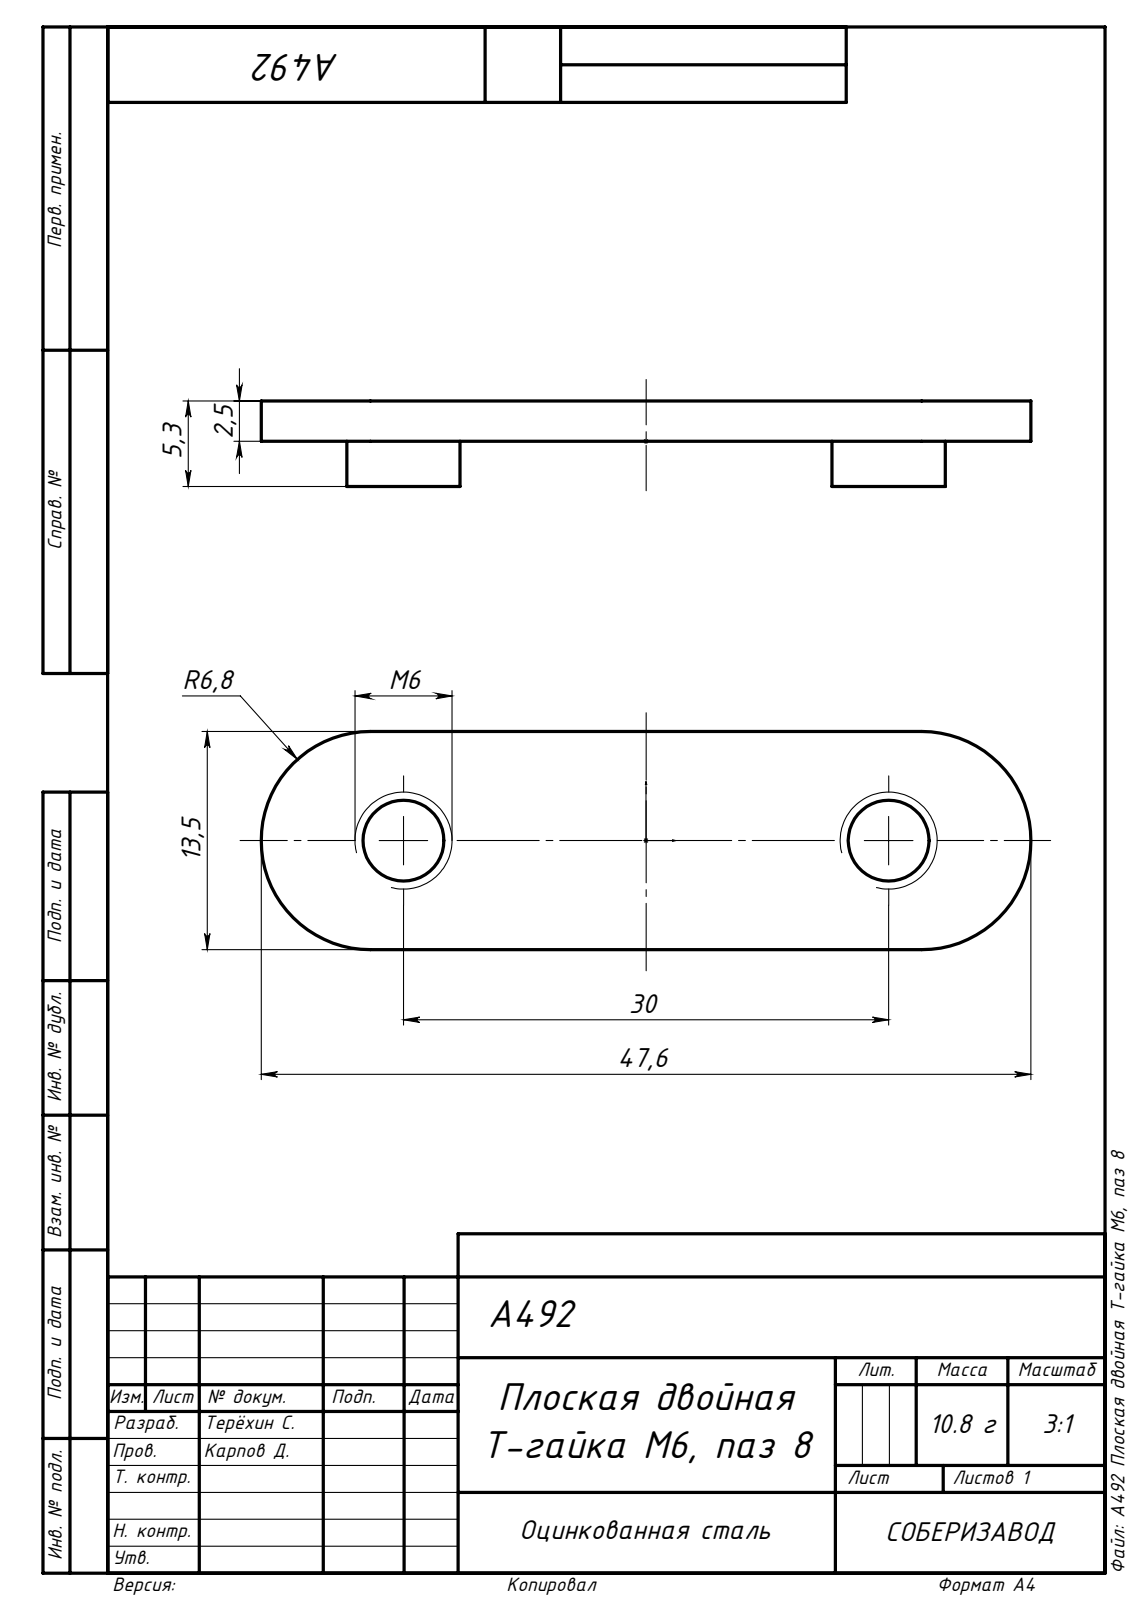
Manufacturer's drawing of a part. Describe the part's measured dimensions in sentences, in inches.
The part is named "A492 Плоская двойная Т-гайка М6, паз 8". Its 3-D file was written by "SolidWorks 2021 (AUTOMOTIVE_DESIGN)". It is 1 solid with 21 faces: 6 planar, 11 cylindrical and 4 other. Overall it measures 1.874 by 0.531 by 0.209 inches. Its volume is 0.092 cubic inches and its surface area 2.616 square inches. Round holes: 2 of diameter 0.197. Round bosses or shafts: 2 of diameter 0.276. Partial cylindrical surfaces (rounded edges, fillets, slot ends): 2 of radius 0.266. The main face-to-face distances are 0.098, 0.531, 0.11, 0.209. The hole center spacings are 1.181.
